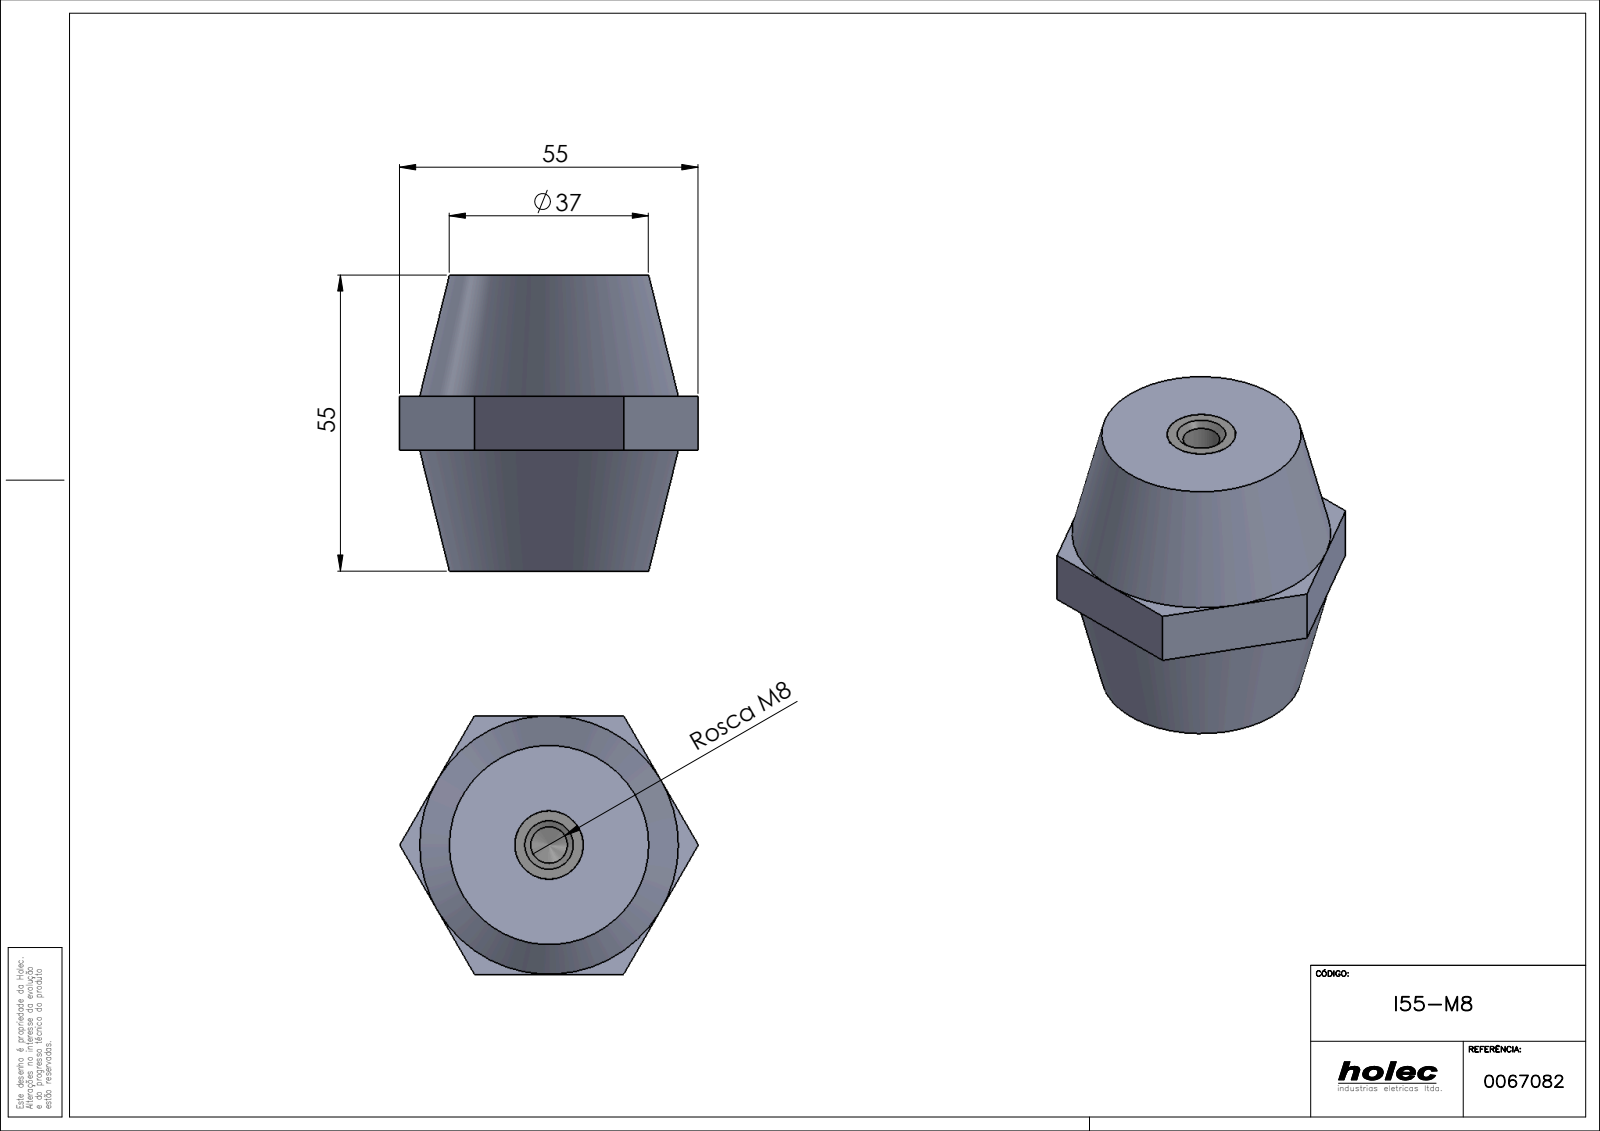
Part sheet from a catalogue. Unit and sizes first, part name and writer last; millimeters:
Units: millimetres
Overall size (bounding box): 55.43 × 55 × 48
Round holes (diameter × count): ⌀6.8 ×1, ⌀10 ×1
Main face-to-face distances: 55, 48, 12.7, 41.01, 41, 22.5, 32.5, 9, 5, 13.99
Volume: 83 240 mm³ · Surface area: 14 132 mm²
Bodies: 3 solids, 154 faces (82 planar, 12 cylindrical, 60 other)
Part name (STEP PRODUCT): PB1_0005; PB1_0107(PB1_0106_08); I55-M8
STEP written by: SolidWorks 2017 (AUTOMOTIVE_DESIGN)
